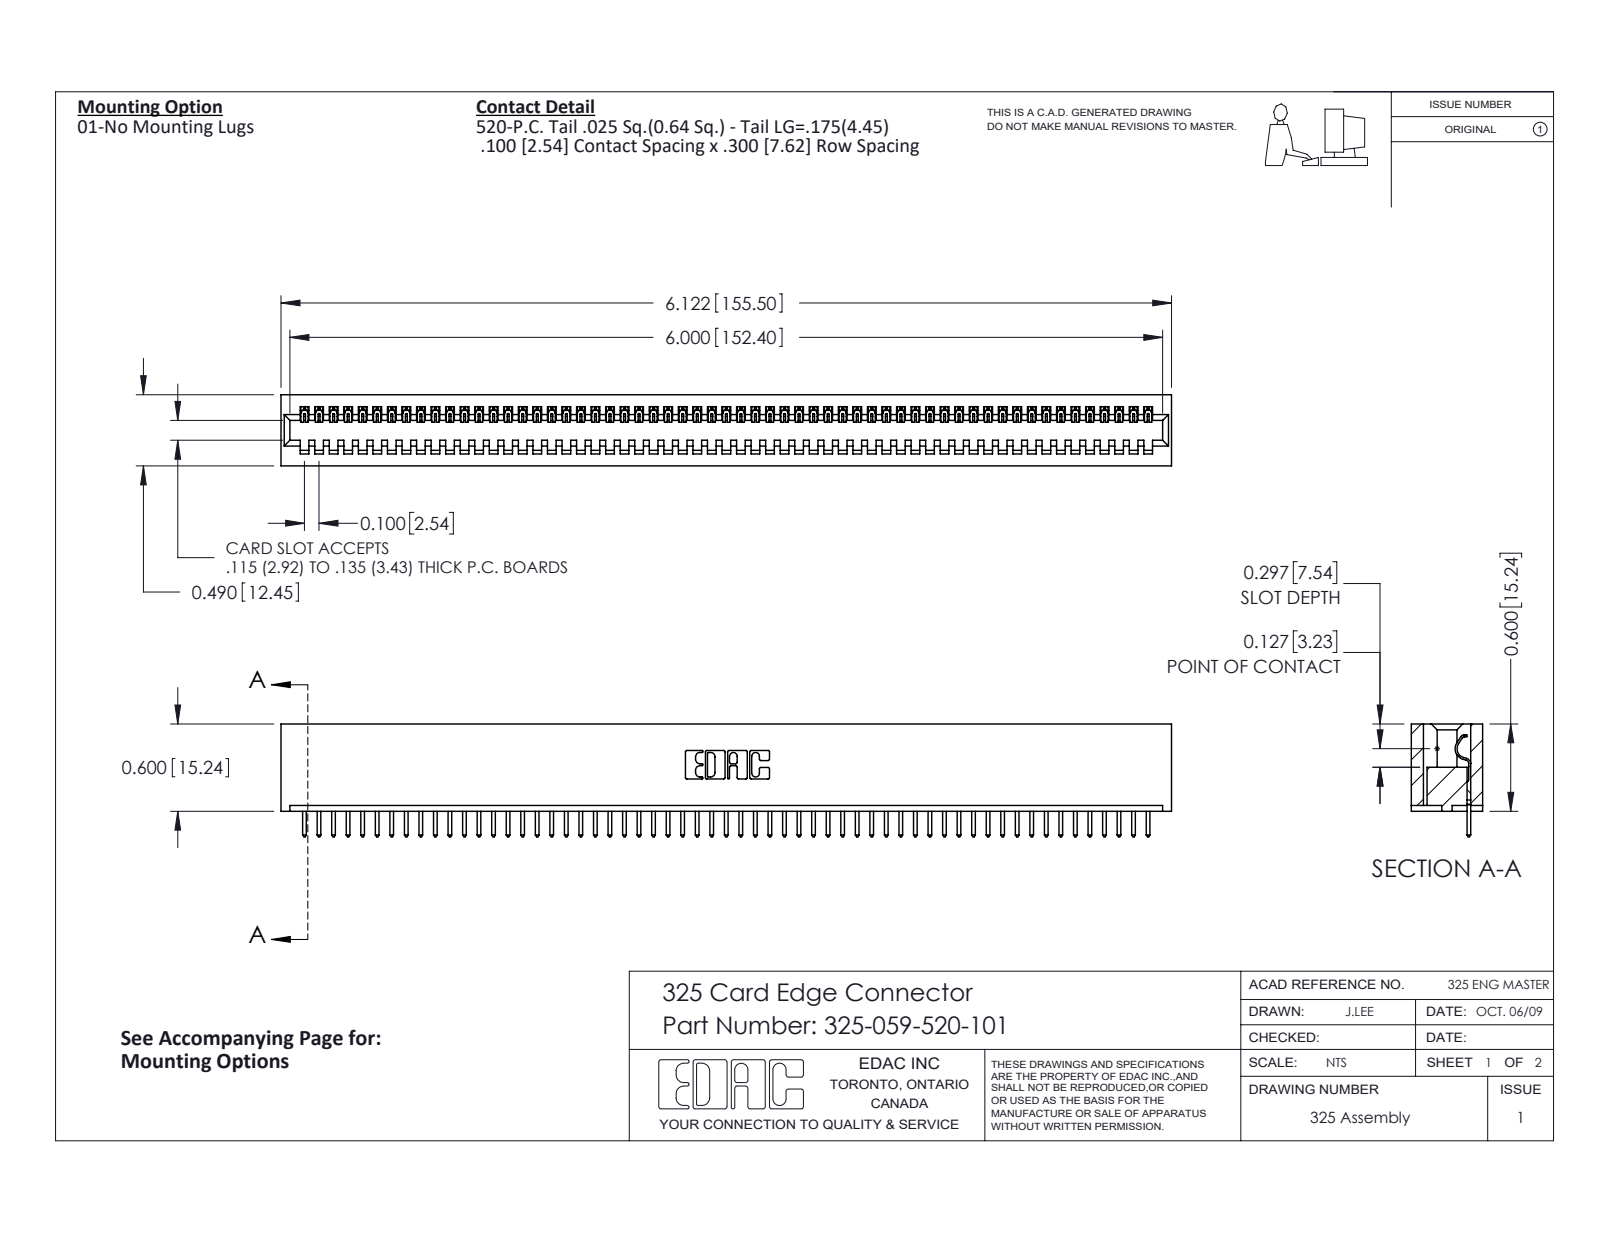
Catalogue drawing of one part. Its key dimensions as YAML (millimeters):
part_name: "325 Part_Lugless; 325-059-520-101; 325-292-001_325-293-120"
step_written_by: "SolidWorks 2016 (CONFIG_CONTROL_DESIGN)"
units: millimeters
bodies: {solids: 60, faces: 3528, planar: 2544, cylindrical: 984, other: 0}
overall_size: [155.5, 19.7, 12.4]
volume: 20290
surface_area: 22330
partial_cylinders:
  - {radius: 0.2, count: 118}
  - {radius: 0.3, count: 118}
  - {radius: 0.3, count: 22}
  - {radius: 0.2, count: 6}
  - {radius: 0.8, count: 6}
  - {radius: 0.7, count: 3}
  - {radius: 0.4, count: 1}
  - {radius: 0.6, count: 1}
face_to_face_distances: [2.1, 10.3, 12.4, 7.6, 2.7, 9.7, 0.6, 8.3, 14.2, 6.7]
